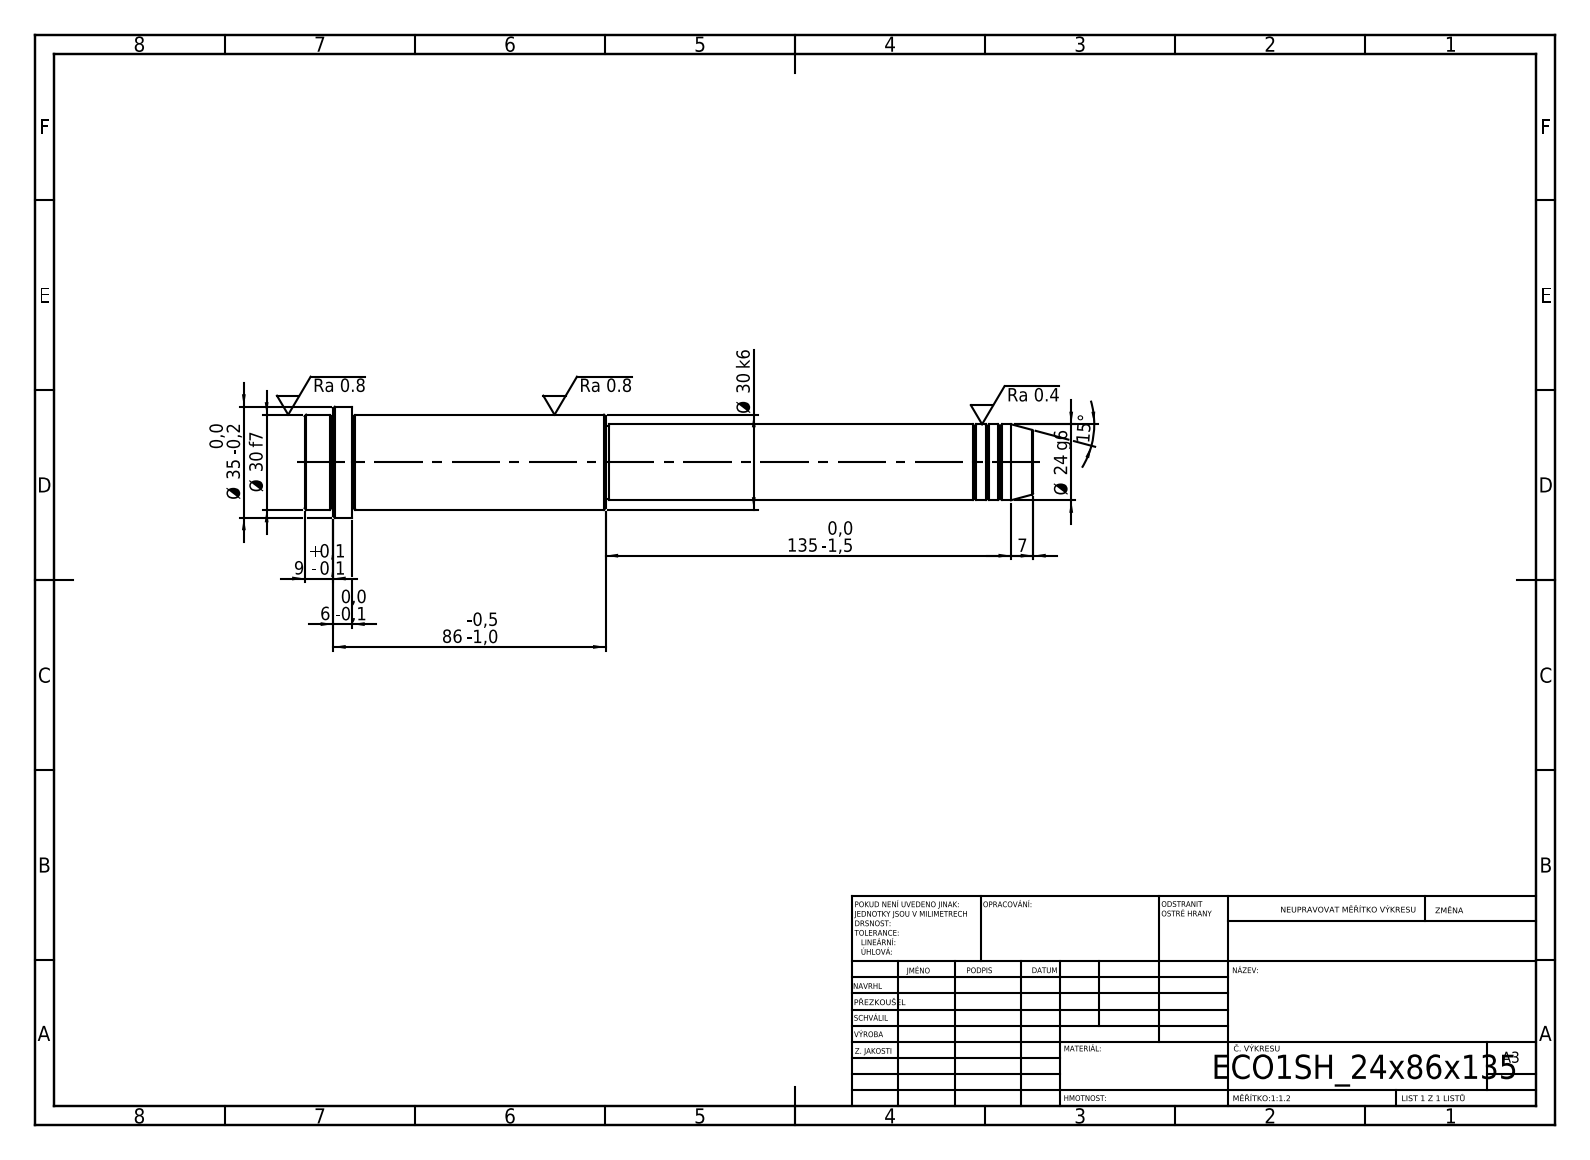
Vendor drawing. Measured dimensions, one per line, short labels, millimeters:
written by: SolidWorks 2019 (CONFIG_CONTROL_DESIGN)
unit: mm
bodies: 1 solid, 52 faces (6 planar, 16 cylindrical, 30 other)
size: 230 × 35 × 35
volume: 129 051 mm³; area: 21 192 mm²
bosses: 1× ⌀35, 1× ⌀30, 1× ⌀24, 1× ⌀23
face distances: 230, 215, 15, 135, 80, 95, 221, 86, 6, 9
